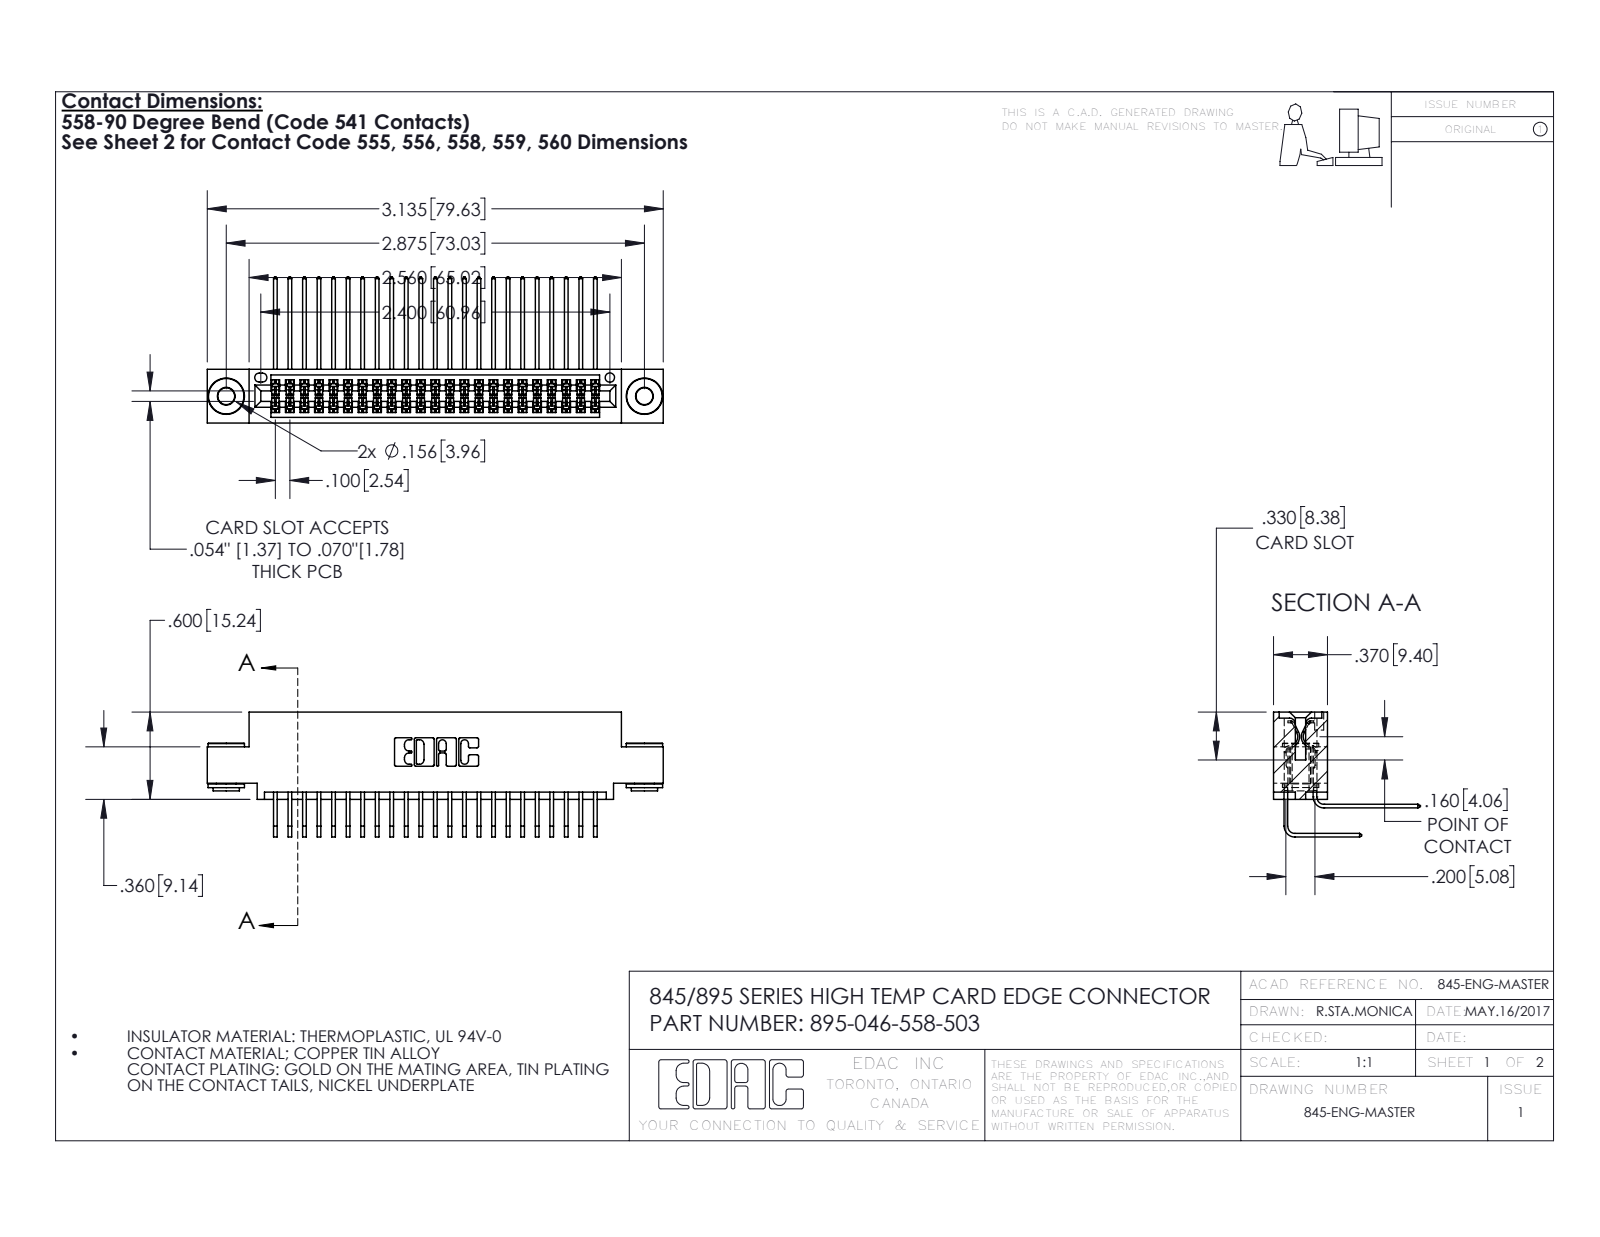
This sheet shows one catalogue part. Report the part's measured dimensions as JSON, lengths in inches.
{"part_name": "345-250-002_345-250-002-102; 345-292-001_558 Tail - 2; 345-292-001_558 559 Tail - 1; 395-046-558-503 (+1 more)", "step_written_by": "SolidWorks 2016 (CONFIG_CONTROL_DESIGN)", "units": "inches", "bodies": {"solids": 49, "faces": 2560, "planar": 1704, "cylindrical": 848, "other": 8}, "overall_size": [3.135, 1.005, 0.859], "volume_in3": 0.474, "surface_area_in2": 19.63, "round_holes": [[0.116, 2], [0.156, 2], [0.064, 1]], "round_bosses_or_shafts": [[0.25, 2], [0.18, 2], [0.136, 2]], "partial_cylinders_radius": [[0.006, 92], [0.01, 22], [0.007, 6], [0.031, 6], [0.026, 3], [0.014, 2], [0.019, 2], [0.022, 2]], "face_to_face_distances": [0.072, 0.298, 0.2, 0.37, 0.025, 0.098, 0.272, 0.225, 0.025, 0.175], "hole_center_spacings": [0.27, 2.641, 2.875]}
